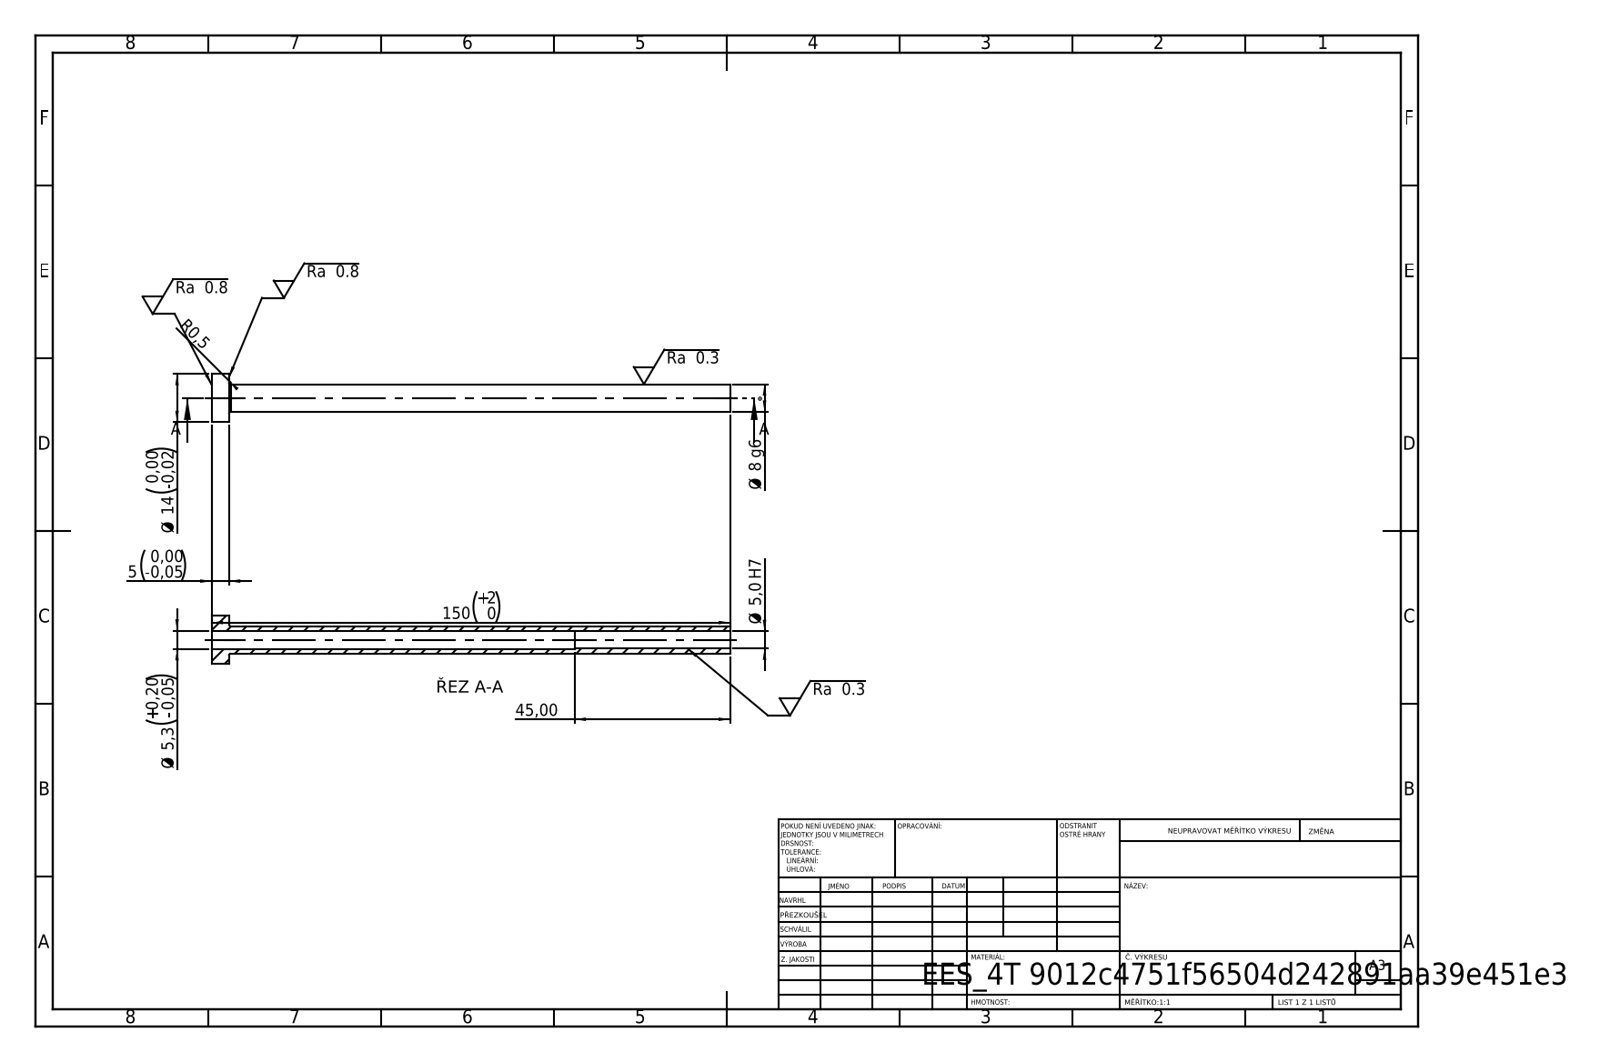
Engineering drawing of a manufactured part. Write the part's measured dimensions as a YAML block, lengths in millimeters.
step_written_by: "SolidWorks 2019 (CONFIG_CONTROL_DESIGN)"
units: millimeters
bodies: {solids: 1, faces: 14, planar: 4, cylindrical: 8, other: 2}
overall_size: [150, 14, 14]
volume: 4860
surface_area: 6583
round_holes:
  - {diameter: 5, count: 1}
  - {diameter: 5.3, count: 1}
round_bosses_or_shafts:
  - {diameter: 14, count: 1}
  - {diameter: 8, count: 1}
face_to_face_distances: [5, 150, 145, 105, 100, 45]
